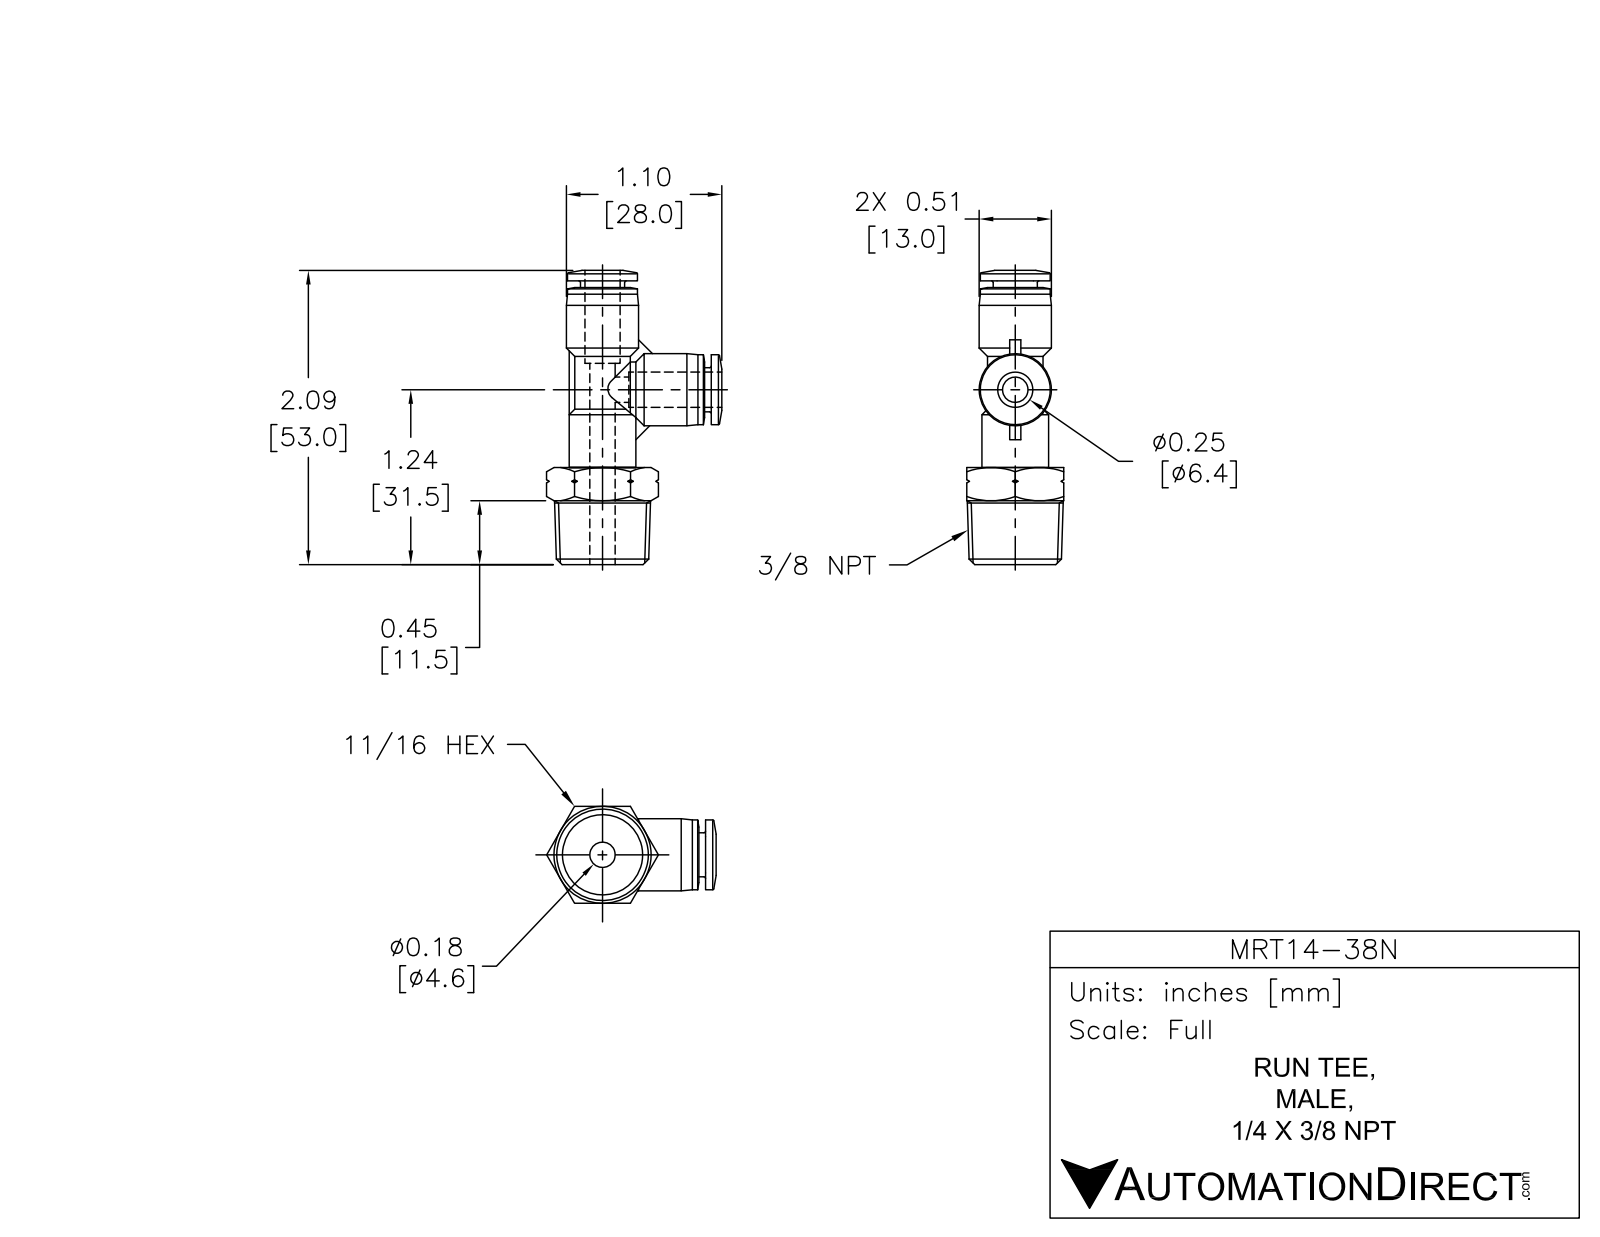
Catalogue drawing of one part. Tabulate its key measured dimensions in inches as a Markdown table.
| quantity | value |
| --- | --- |
| part name | MRT14-38N |
| STEP written by | SolidWorks 2015 (AUTOMOTIVE_DESIGN) |
| units | inches |
| bodies | 1 solid, 119 faces (23 planar, 30 cylindrical, 66 other) |
| overall size | 2.087 × 1.243 × 0.687 |
| volume | 0.508 in³ |
| surface area | 7.581 in² |
| round holes (diameter × count) | 0.157 × 2, 0.258 × 2 |
| round bosses / shafts (diameter × count) | 0.512 × 2, 0.496 × 2, 0.394 × 2, 0.313 × 2, 0.472 × 1 |
| main face-to-face distances | 0.687, 0.689, 2.012, 1.323, 0.047, 0.304, 0.383, 0.539, 0.587, 1.965 |
